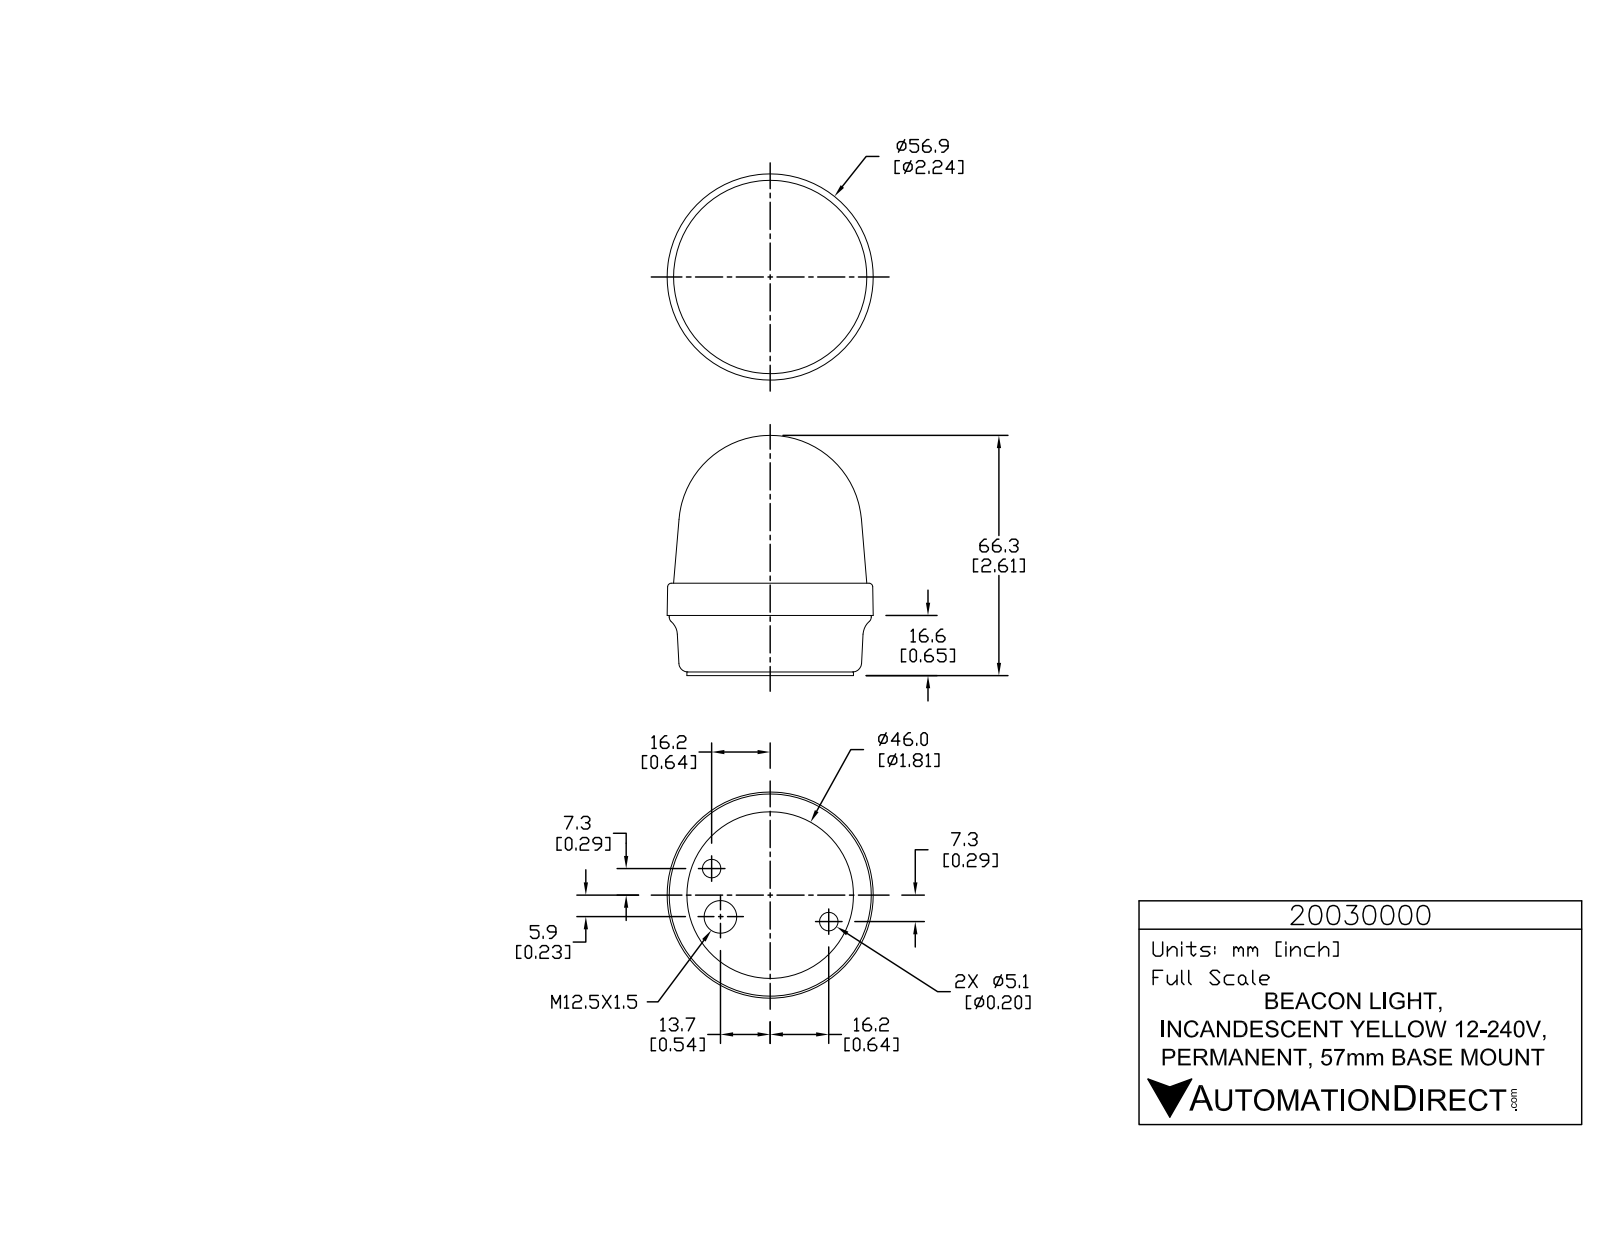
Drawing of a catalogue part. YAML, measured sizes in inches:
part_name: "20030000"
step_written_by: "SolidWorks 2015 (AUTOMOTIVE_DESIGN)"
units: inches
bodies: {solids: 1, faces: 781, planar: 526, cylindrical: 163, other: 92}
overall_size: [2.61, 2.24, 2.24]
volume: 7.533
surface_area: 20.69
round_holes:
  - {diameter: 0.039, count: 3}
  - {diameter: 0.201, count: 2}
  - {diameter: 0.354, count: 1}
round_bosses_or_shafts:
  - {diameter: 0.226, count: 3}
  - {diameter: 0.056, count: 3}
  - {diameter: 2.197, count: 1}
  - {diameter: 1.811, count: 1}
partial_cylinders:
  - {radius: 0.008, count: 6}
  - {radius: 0.008, count: 6}
  - {radius: 0.008, count: 6}
  - {radius: 0.131, count: 6}
  - {radius: 0.004, count: 3}
  - {radius: 0.005, count: 3}
  - {radius: 0.008, count: 3}
  - {radius: 0.008, count: 3}
face_to_face_distances: [0.039, 0.654, 0.614, 1.004, 0.965, 0.35, 0.697, 1.351, 1.311, 0.347]
hole_center_spacings: [0.534, 1.179, 1.398]
